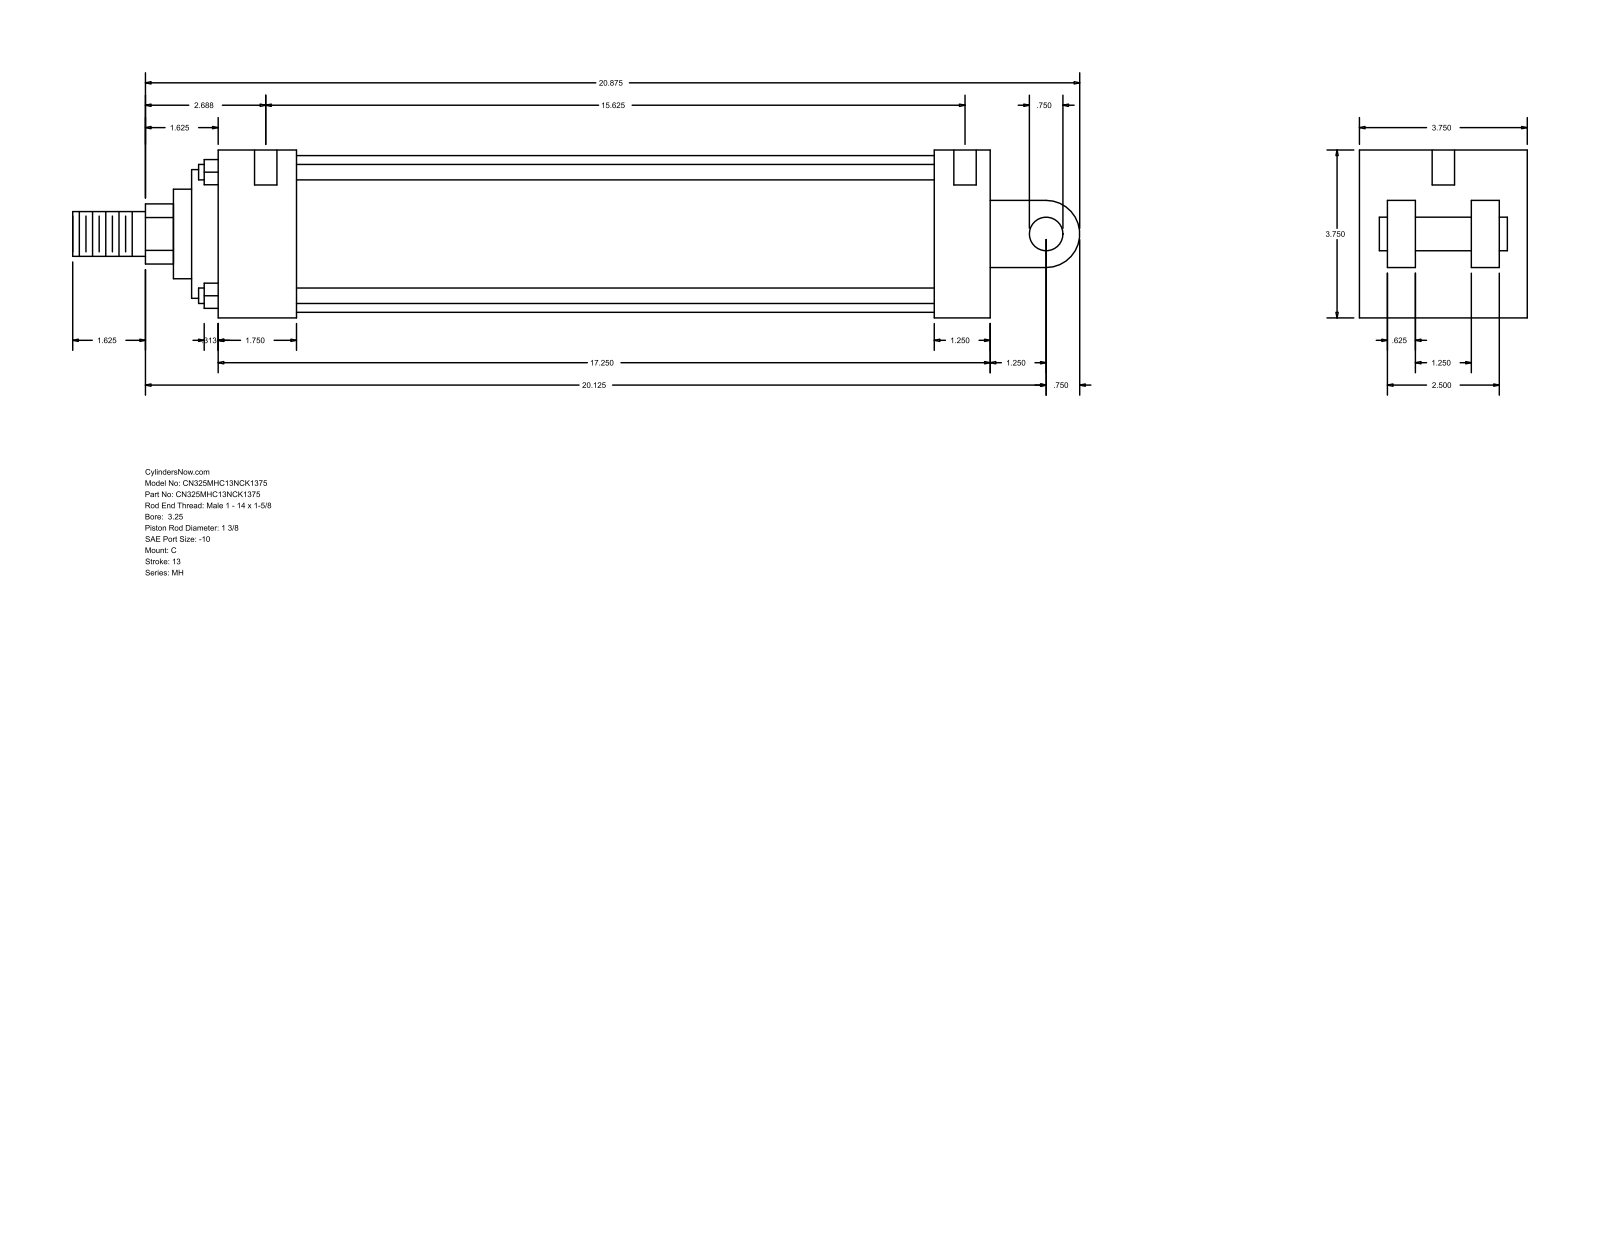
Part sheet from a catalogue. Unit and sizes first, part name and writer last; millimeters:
Units: millimetres
Overall size (bounding box): 571.5 × 95.25 × 95.25
Round holes (diameter × count): ⌀5.56 ×4, ⌀12.7 ×2
Round bosses / shafts (diameter × count): ⌀8.76 ×4, ⌀88.9 ×1, ⌀73.03 ×1, ⌀50.8 ×1, ⌀34.92 ×1, ⌀25.4 ×1, ⌀19.05 ×1
Partial cylindrical surfaces — rounded edges, fillets, slot ends (radius × count): R17.06 ×1, R19.05 ×1
Main face-to-face distances: 95.24, 15.87, 63.5, 438.16, 79.37, 31.74, 47.63, 44.45, 406.41, 361.96
Hole centre spacings: 403.23, 1.59, 4.76, 396.88, 398.47, 401.64
Bodies: 0 solids, 101 faces (71 planar, 30 cylindrical, 0 other)
Part name (STEP PRODUCT): MH_C__0325_1.375
STEP written by: GSSL Pune (CONFIG_CONTROL_DESIGN)
